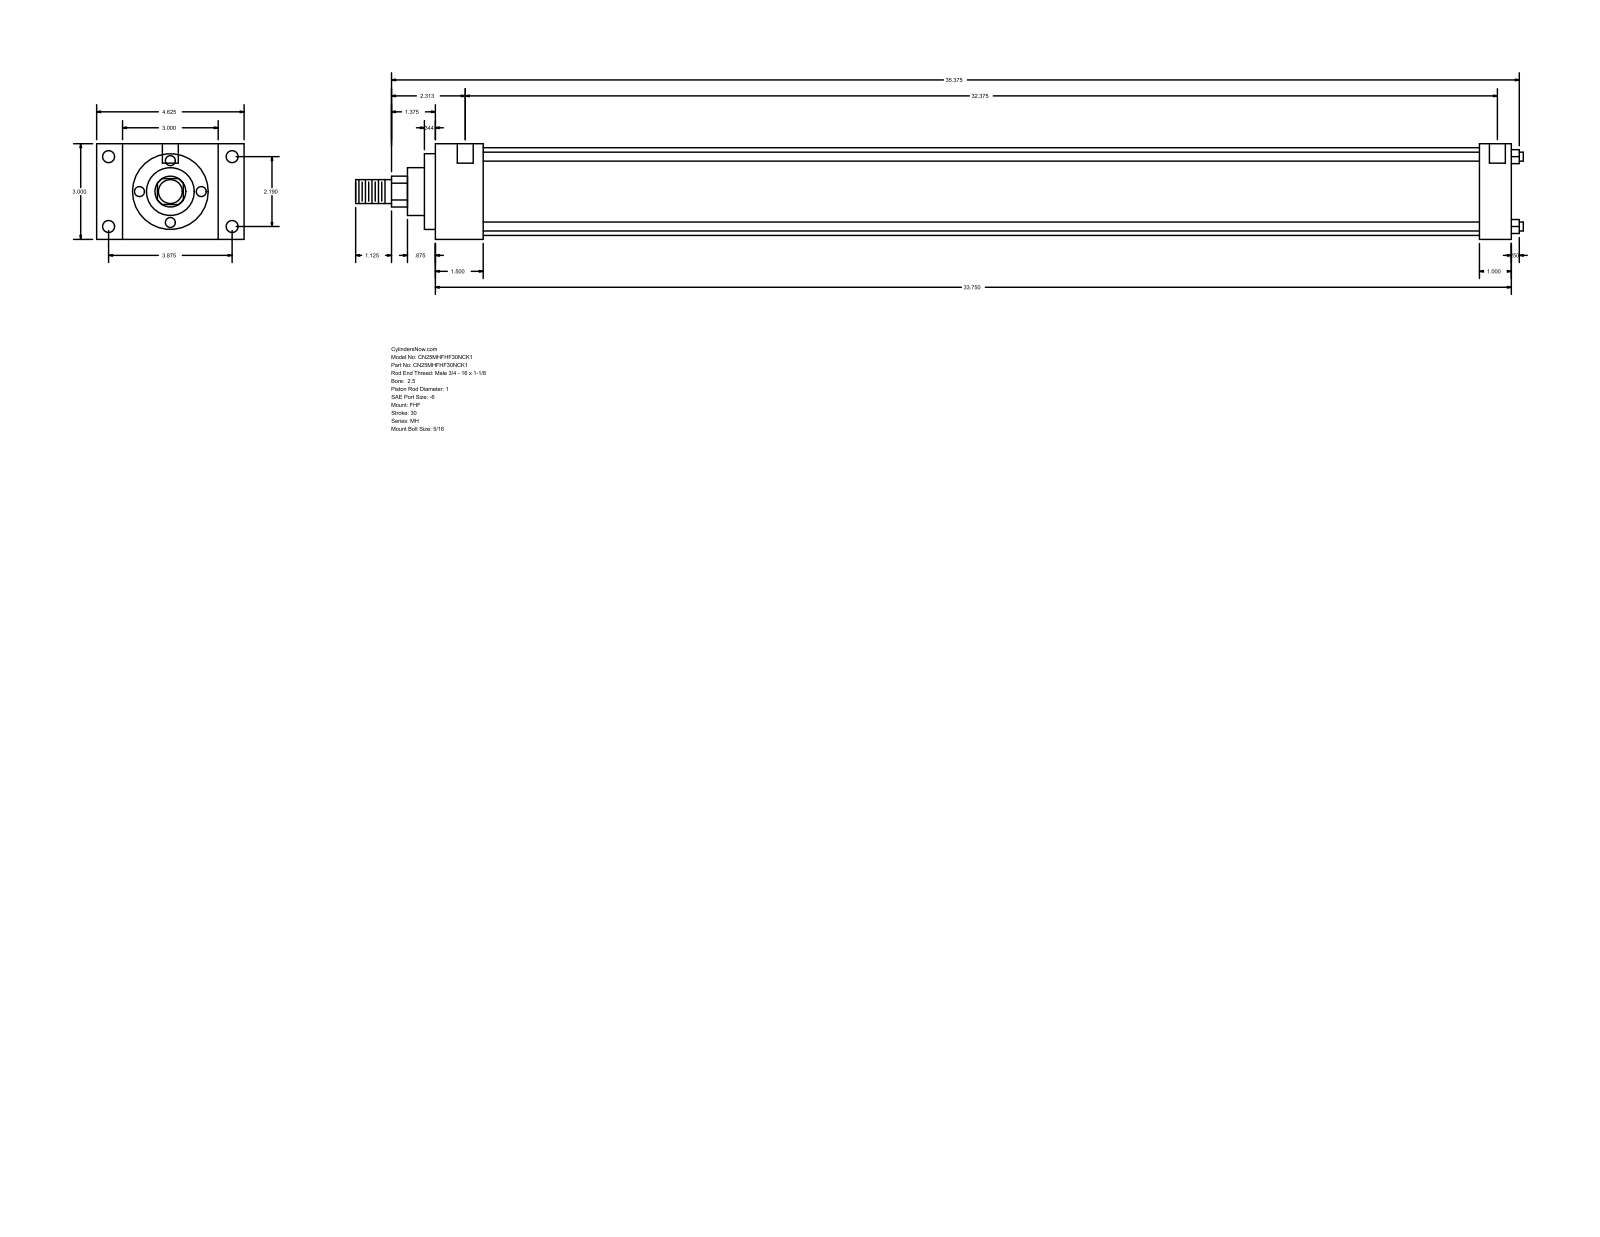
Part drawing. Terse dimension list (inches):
name: MH_FHF__0250_1
written by: GSSL Pune (CONFIG_CONTROL_DESIGN)
unit: in
bodies: 0 solids, 90 faces (61 planar, 29 cylindrical, 0 other)
size: 36.625 × 4.625 × 3
holes: 4× ⌀0.219, 4× ⌀0.375, 2× ⌀0.5
bosses: 4× ⌀0.281, 1× ⌀2.75, 1× ⌀2.375, 1× ⌀1.5, 1× ⌀1, 1× ⌀0.75
rounds: 1× R0.484
face distances: 3, 33.75, 1.5, 32.25, 0.813, 3.813, 4.625, 32.75, 31.25, 1
hole spacings: 2.19, 3.875, 4.451, 32.687, 0.125, 0.187, 32.375, 32.5
